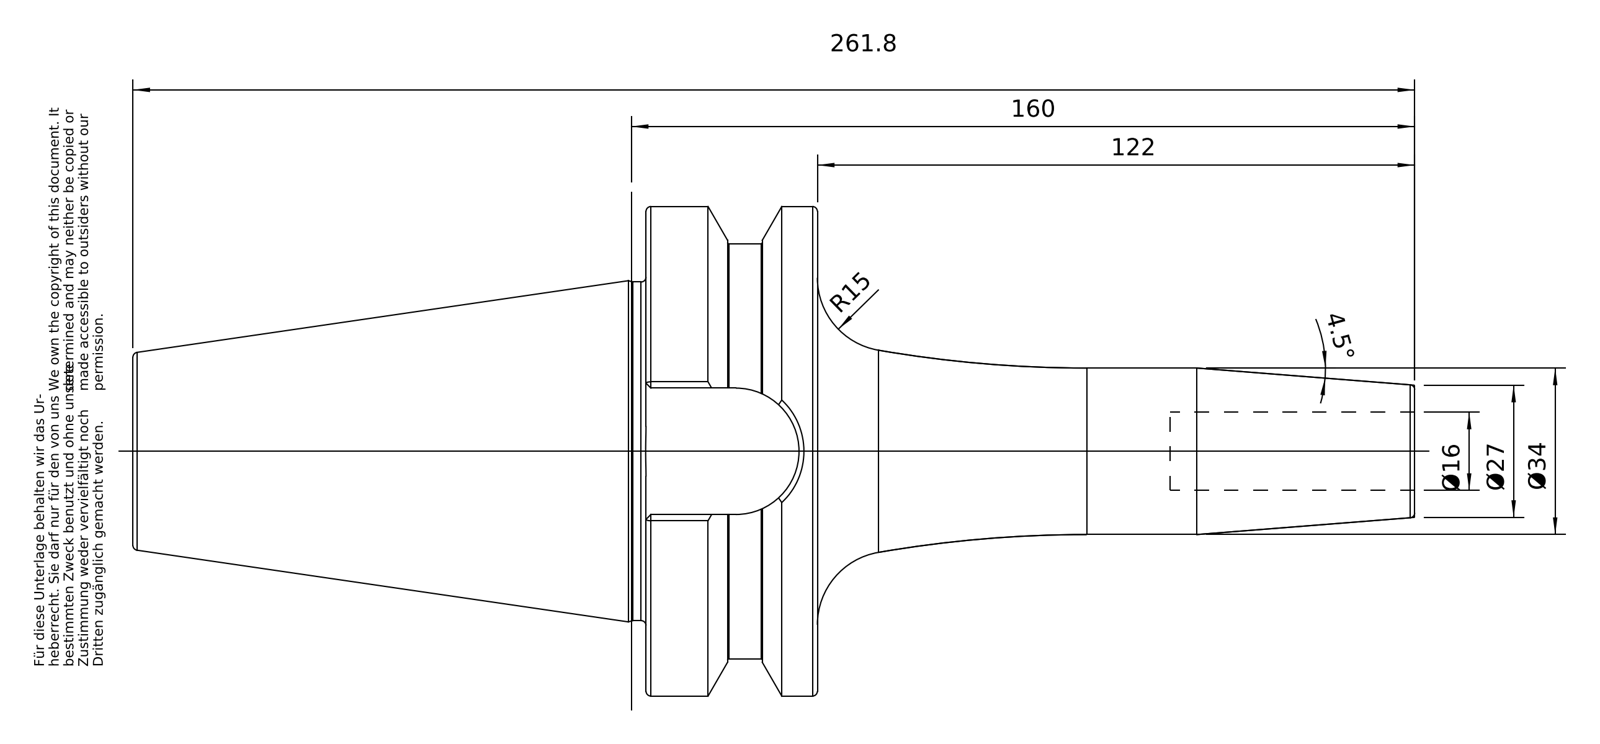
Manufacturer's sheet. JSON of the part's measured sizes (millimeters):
{"part_name": "50-642-16", "step_written_by": "PRO/ENGINEER BY PARAMETRIC TECHNOLOGY CORPORATION, 2010430 (CONFIG_CONTROL_DESIGN)", "units": "millimeters", "bodies": {"solids": 1, "faces": 98, "planar": 26, "cylindrical": 22, "other": 50}, "overall_size": [261.8, 99.97, 99.97], "volume_mm3": 579078, "surface_area_mm2": 66036, "round_holes": [[16, 1], [20.75, 1], [25.02, 1], [25.7, 1]], "round_bosses_or_shafts": [[99.97, 1], [84.75, 1], [69.15, 1], [34, 1], [24.01, 1]], "partial_cylinders_radius": [[12.9, 1]], "face_to_face_distances": [35, 70.4, 104.8, 139.8, 25.8, 261.8, 157, 122, 211.8, 107]}
